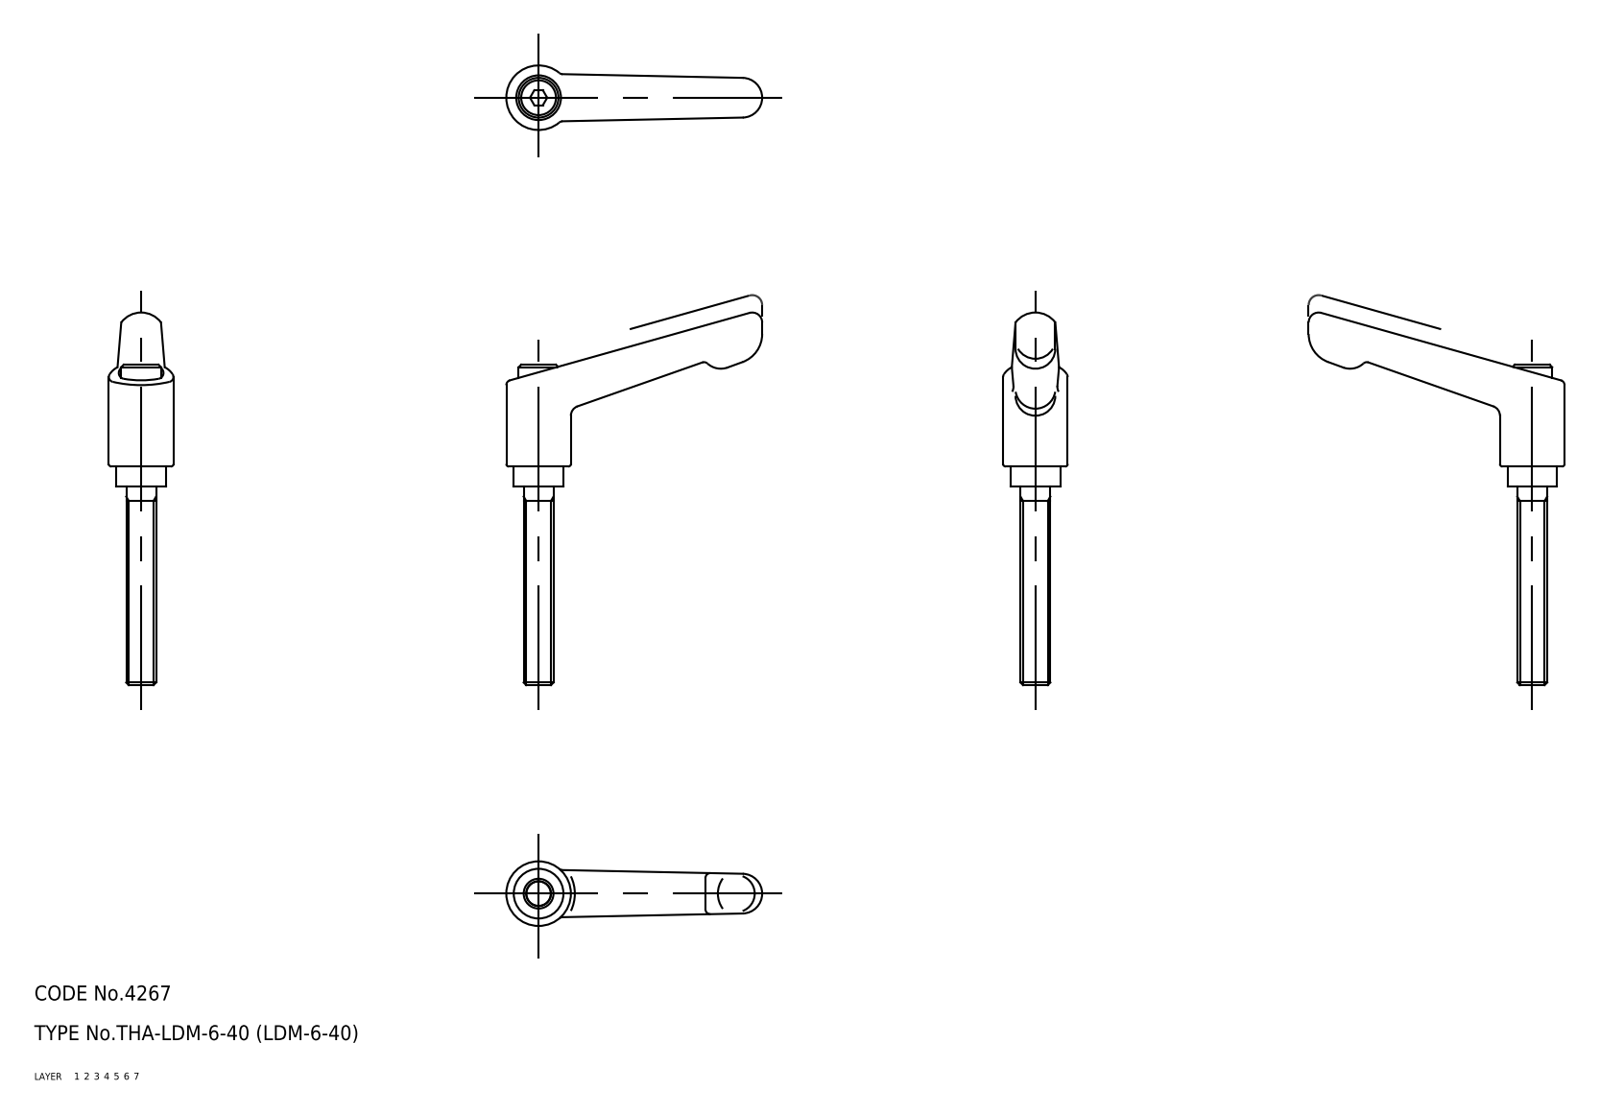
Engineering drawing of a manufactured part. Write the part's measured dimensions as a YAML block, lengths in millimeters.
part_name: "sleeve; screw; handle; LDM_6_40_13365_36"
step_written_by: "CADfix (AUTOMOTIVE_DESIGN)"
units: millimeters
bodies: {solids: 3, faces: 70, planar: 0, cylindrical: 0, other: 70}
overall_size: [75, 51.5, 13]
volume: 6262
surface_area: 4269
